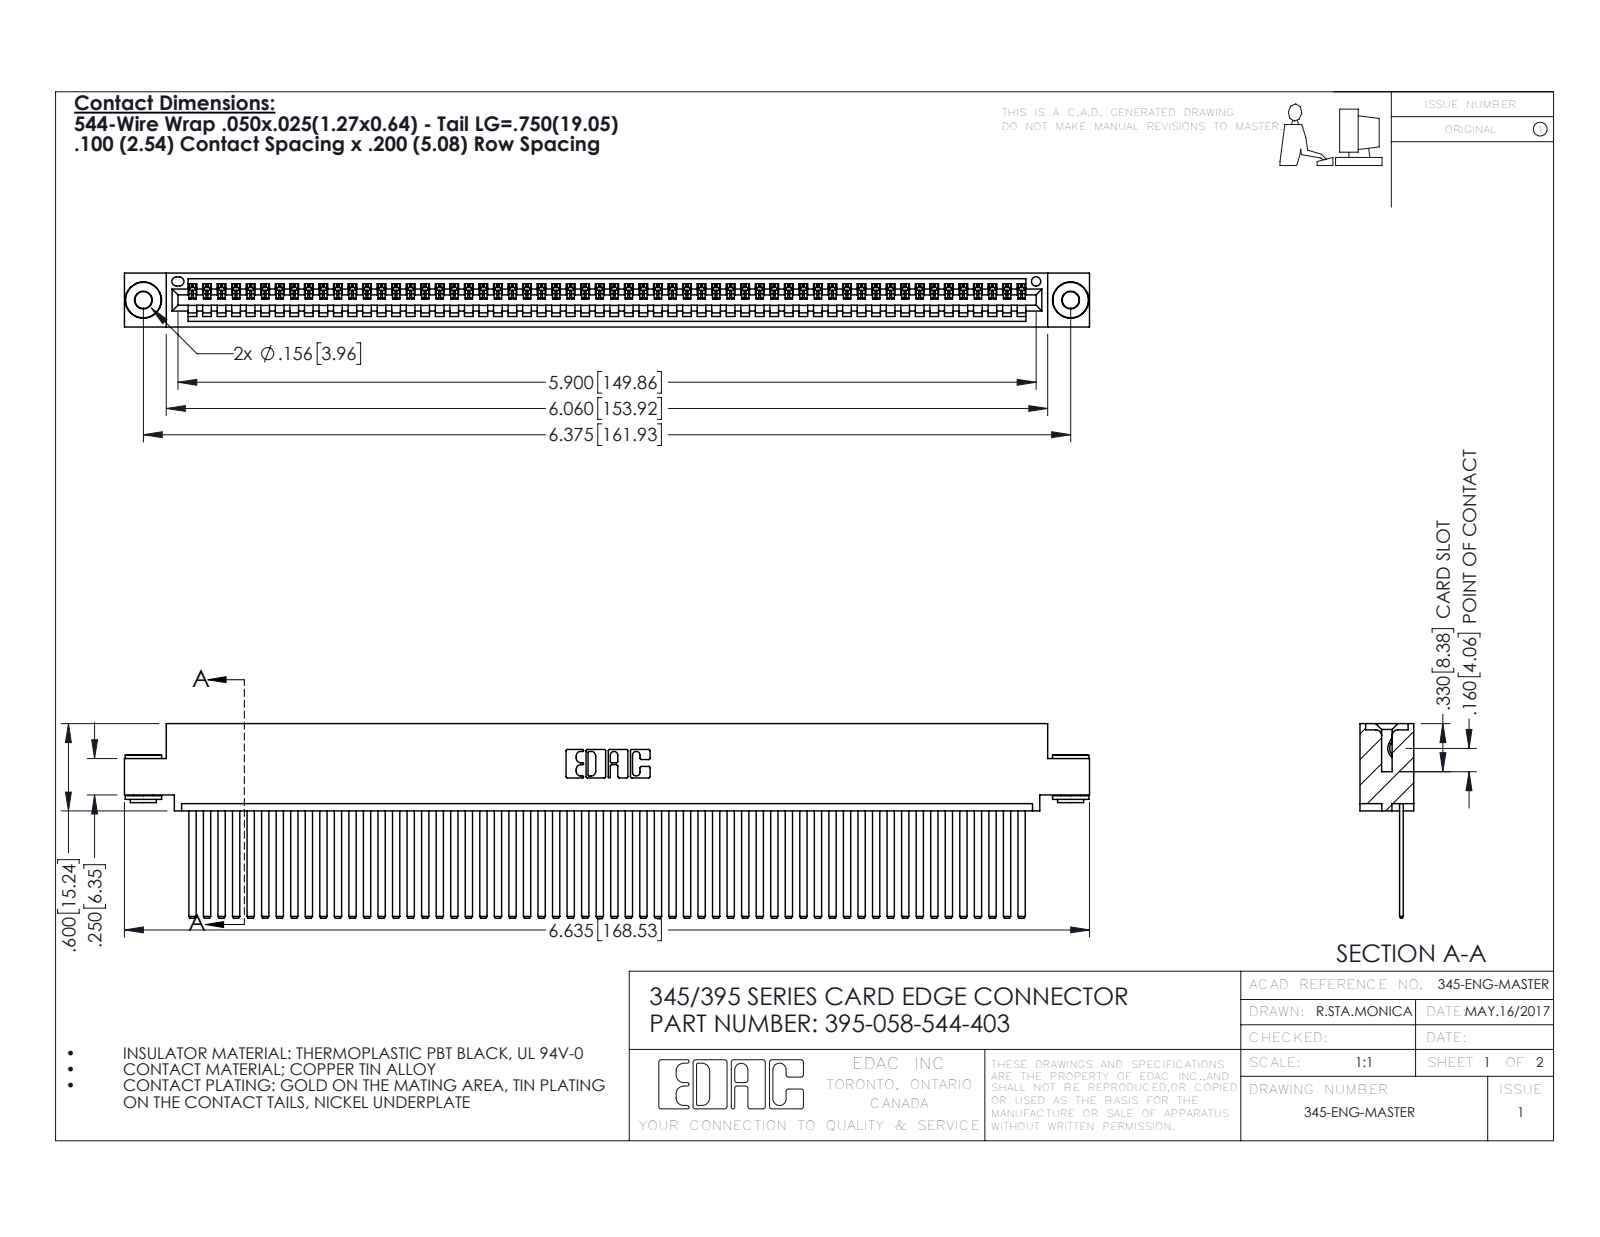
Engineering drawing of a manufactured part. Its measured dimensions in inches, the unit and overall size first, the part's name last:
Units: inches
Overall size (bounding box): 6.635 × 1.337 × 0.37
Round holes (diameter × count): ⌀0.116 ×2, ⌀0.156 ×2, ⌀0.064 ×1
Round bosses / shafts (diameter × count): ⌀0.25 ×2, ⌀0.18 ×2, ⌀0.136 ×2
Partial cylindrical surfaces — rounded edges, fillets, slot ends (radius × count): R0.006 ×116, R0.01 ×22, R0.007 ×6, R0.031 ×6, R0.026 ×3, R0.031 ×2, R0.04 ×2, R0.014 ×1
Main face-to-face distances: 0.072, 0.298, 0.025, 0.098, 0.272, 0.37, 0.2, 0.225, 0.149, 0.072
Hole centre spacings: 0.27, 6.139, 6.375
Volume: 1.023 in³ · Surface area: 38.44 in²
Bodies: 61 solids, 3184 faces (2182 planar, 994 cylindrical, 8 other)
Part name (STEP PRODUCT): 345 Part_0.110 Offset - 0.156 Dia-TH; 345-292-001_345-293-144; 345-250-002_345-250-002-102; 395-058-544-403
STEP written by: SolidWorks 2016 (CONFIG_CONTROL_DESIGN)
